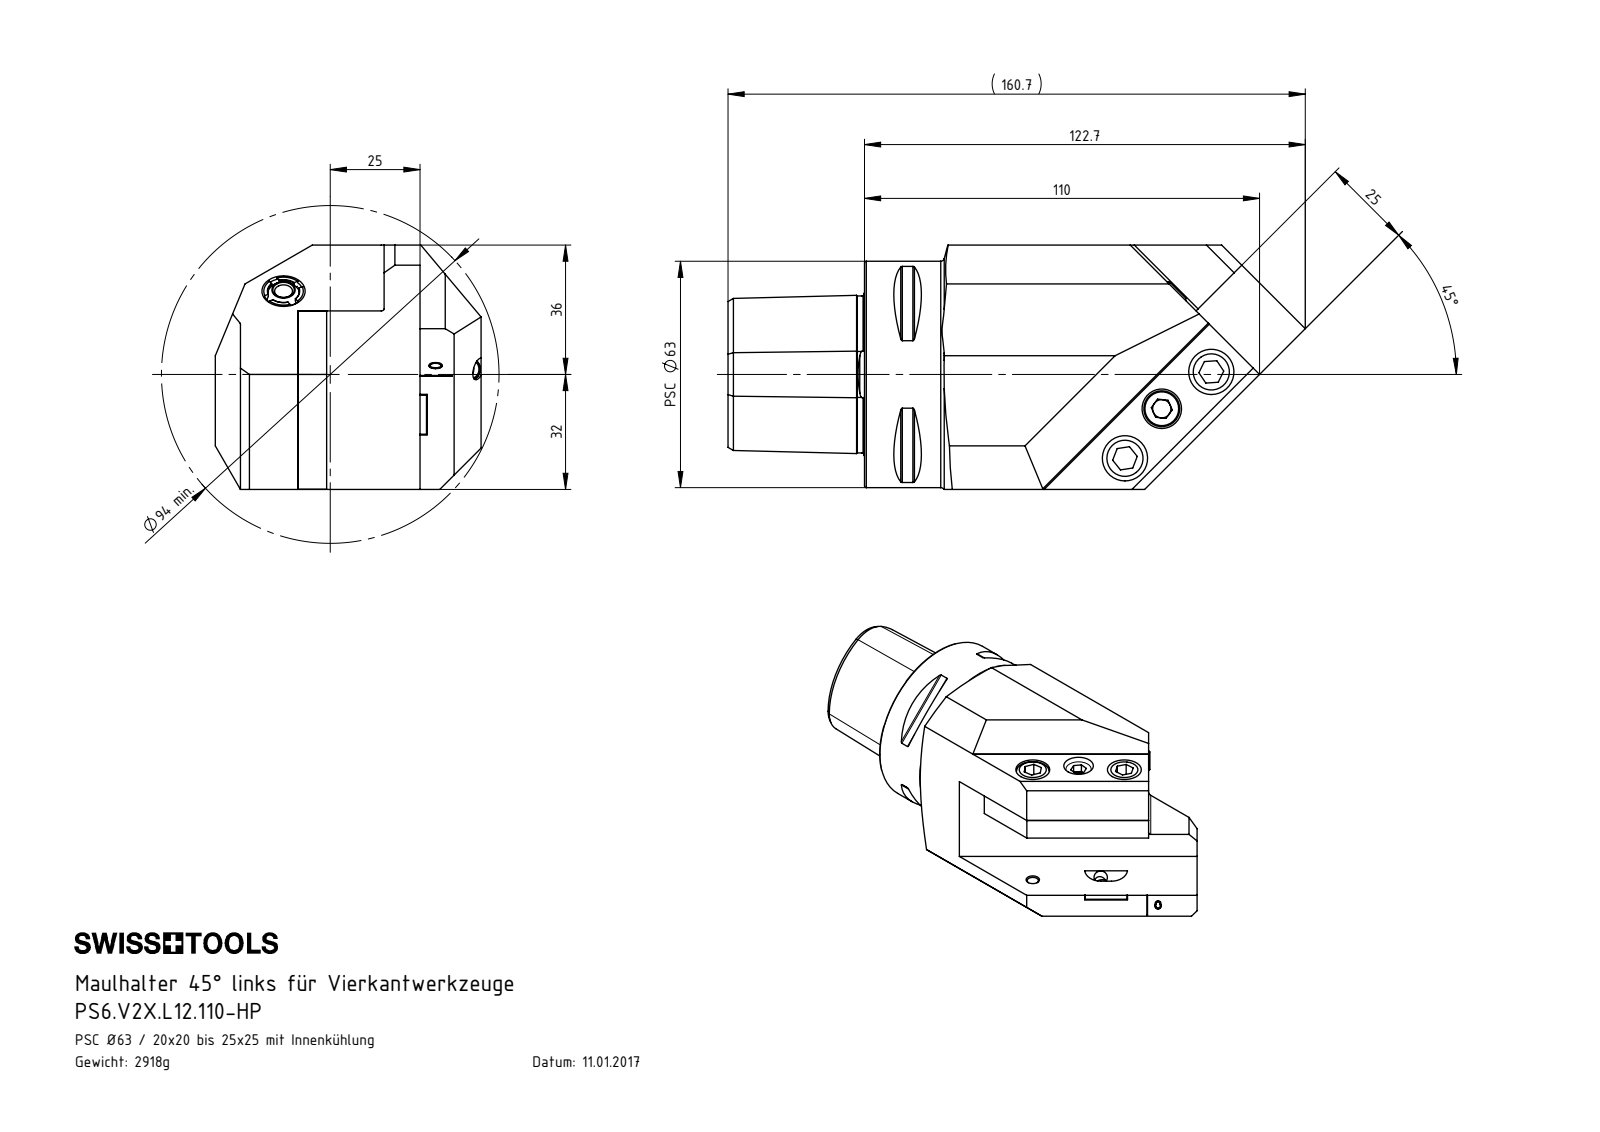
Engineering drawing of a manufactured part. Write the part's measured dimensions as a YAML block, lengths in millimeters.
part_name: "ISO 4762 - M6 x 16_PreviewCfg; 8x1x13_vorgespannt; KVT_MB_600_060; V2X.L12.110-ECO (+7 more)"
step_written_by: "SolidWorks 2017 (AUTOMOTIVE_DESIGN)"
units: millimeters
bodies: {solids: 12, faces: 302, planar: 125, cylindrical: 64, other: 113}
overall_size: [160.73, 74, 68]
volume: 371766
surface_area: 54992
round_holes:
  - {diameter: 5, count: 6}
  - {diameter: 10.2, count: 2}
  - {diameter: 11, count: 2}
  - {diameter: 4, count: 1}
  - {diameter: 4.2, count: 1}
  - {diameter: 6, count: 1}
  - {diameter: 6.8, count: 1}
  - {diameter: 8.1, count: 1}
  - {diameter: 8.5, count: 1}
  - {diameter: 10, count: 1}
  - {diameter: 18, count: 1}
  - {diameter: 28, count: 1}
round_bosses_or_shafts:
  - {diameter: 12, count: 3}
  - {diameter: 6, count: 2}
  - {diameter: 63, count: 1}
  - {diameter: 10, count: 1}
partial_cylinders:
  - {radius: 0.5, count: 8}
  - {radius: 6, count: 3}
  - {radius: 0.8, count: 2}
  - {radius: 4.4, count: 1}
face_to_face_distances: [34, 68, 25, 8, 51, 17, 43, 26, 16, 24]
hole_center_spacings: [17.18, 27.5, 34, 64.86, 71.42, 84.56, 91.06, 98.74]
